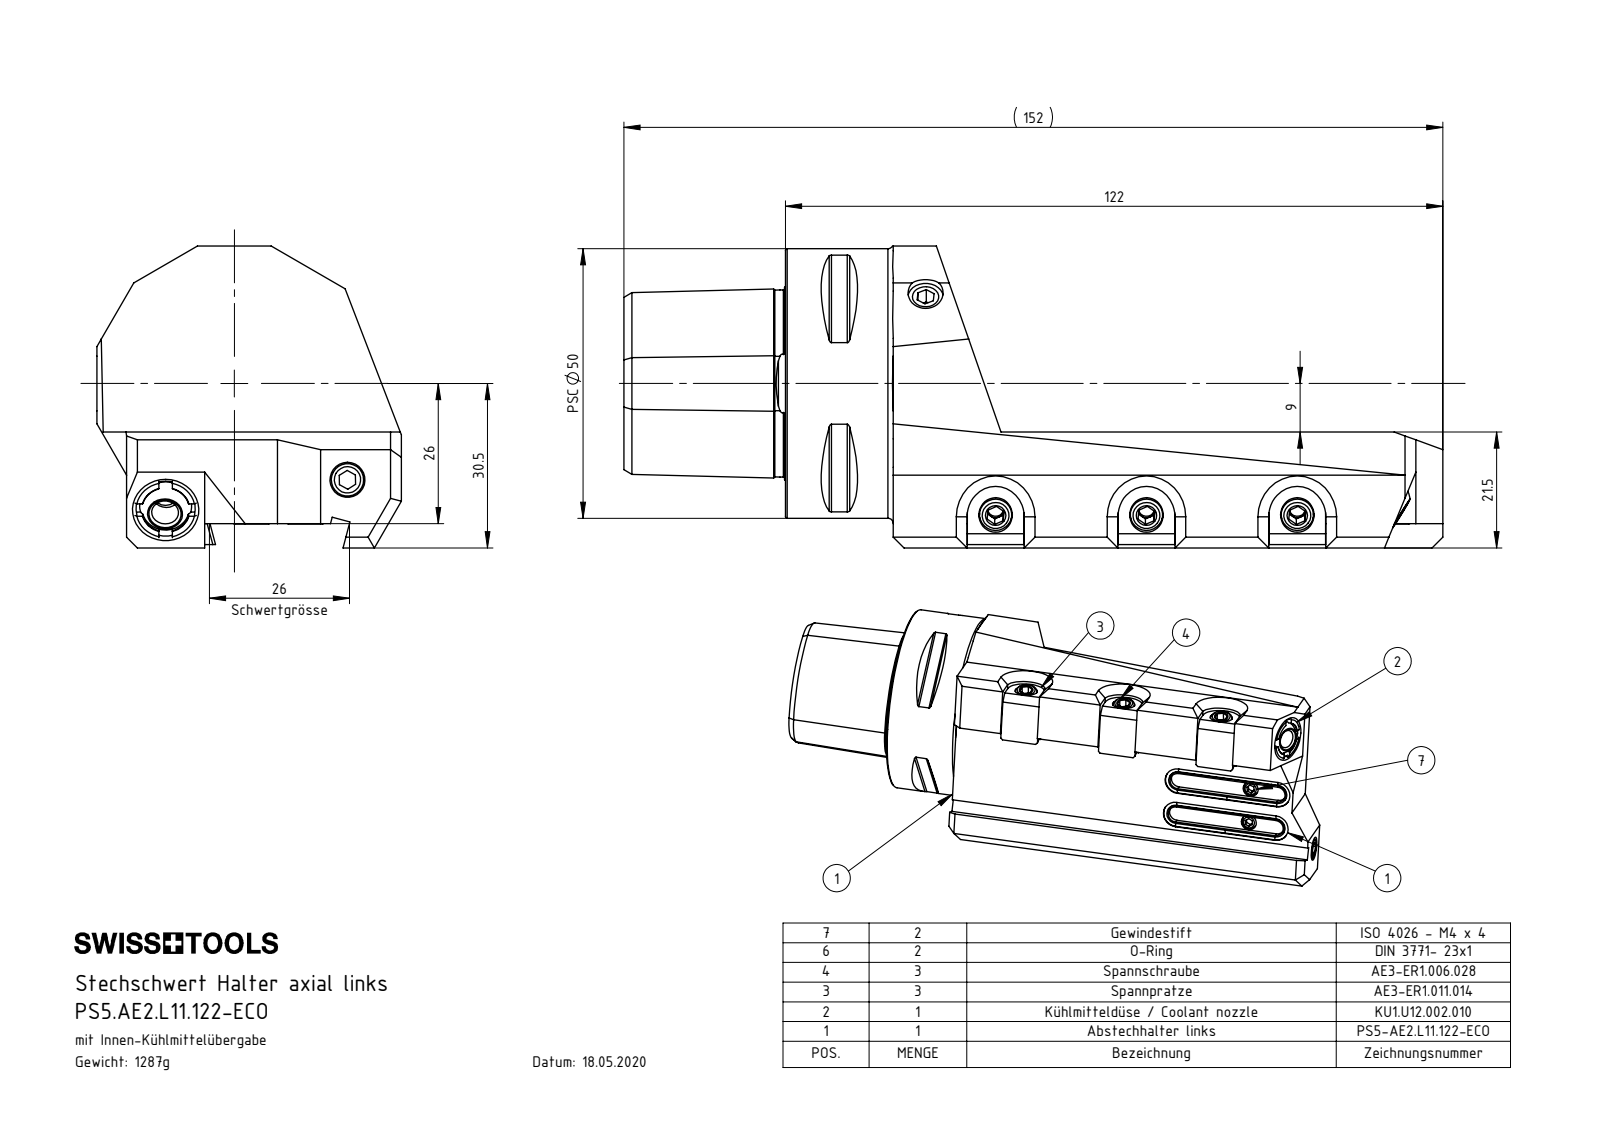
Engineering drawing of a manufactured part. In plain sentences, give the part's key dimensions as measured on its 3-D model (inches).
The part is named "KU1-U12.003.010_B; AE3-ER1.011.014_A; AE3-ER1.006.028_A; ISO 4026 - M4 x 4 (+7 more)". Its 3-D file was written by "SolidWorks 2017 (AUTOMOTIVE_DESIGN)". It is 17 solids with 612 faces: 243 planar, 156 cylindrical and 213 other. Overall it measures 5.984 by 2.224 by 2.205 inches. Its volume is 10.03 cubic inches and its surface area 63.71 square inches. Round holes: 9 of diameter 0.197, 3 of diameter 0.118, 3 of diameter 0.217, 3 of diameter 0.244, 2 of diameter 0.13, 1 of diameter 0.157, 1 of diameter 0.24, 1 of diameter 0.256, 1 of diameter 0.394, 1 of diameter 0.433, 1 of diameter 0.571, 1 of diameter 0.827. Round bosses or shafts: 6 of diameter 0.236, 4 of diameter 0.039, 3 of diameter 0.177, 2 of diameter 0.157, 1 of diameter 1.969, 1 of diameter 0.472. Partial cylindrical surfaces (rounded edges, fillets, slot ends): 8 of radius 0.02, 4 of radius 0.089, 4 of radius 0.104, 4 of radius 0.144, 3 of radius 0.207, 3 of radius 0.209, 1 of radius 0.157, 1 of radius 0.173. The main face-to-face distances are 0.669, 0.177, 0.846, 1.102, 2.008, 0.415, 2.205, 1.181, 1.969, 0.787. The hole center spacings are 1.102, 2.205, 0.394, 1.024, 1.085, 3.709, 4.718.
